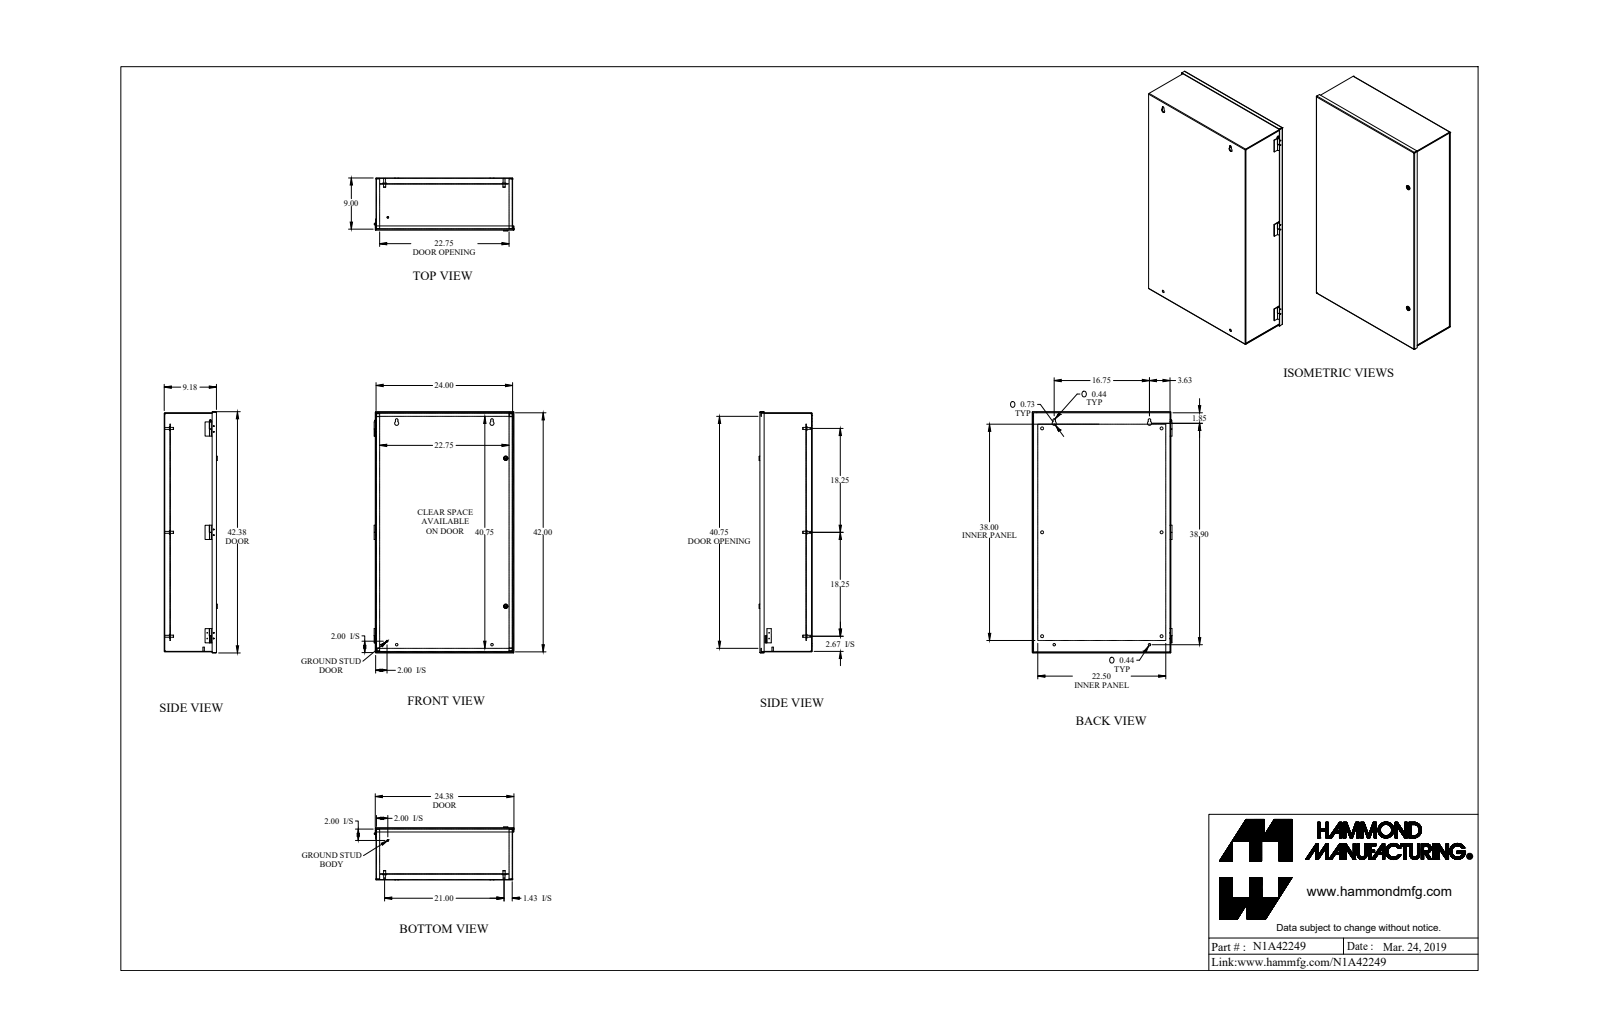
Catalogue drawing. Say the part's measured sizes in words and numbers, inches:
The part is named "N1A42249". Its 3-D file was written by "SolidWorks 2018 (AUTOMOTIVE_DESIGN)". It is 34 solids with 767 faces: 434 planar, 269 cylindrical and 64 other. Overall it measures 42.384 by 24.574 by 9.299 inches. Its volume is 312.8 cubic inches and its surface area 8 712 square inches. Round holes: 12 of diameter 0.14, 6 of diameter 0.5, 4 of diameter 0.307, 4 of diameter 0.445, 2 of diameter 0.437, 2 of diameter 0.516, 2 of diameter 0.734, 1 of diameter 0.17, 1 of diameter 0.187. Round bosses or shafts: 12 of diameter 0.128, 7 of diameter 0.375, 6 of diameter 0.65, 6 of diameter 0.33, 4 of diameter 1, 2 of diameter 0.788, 2 of diameter 0.535, 2 of diameter 0.496. Partial cylindrical surfaces (rounded edges, fillets, slot ends): 16 of radius 0.036, 16 of radius 0.108, 2 of radius 0.06, 2 of radius 0.125, 2 of radius 0.153, 2 of radius 0.219, 2 of radius 0.315, 1 of radius 0.03. The main face-to-face distances are 0.072, 9.105, 1.009, 8.096, 9.033, 9.177, 0.937, 1.081, 8.024, 8.168. The hole center spacings are 1, 1.119, 18.156, 18.25, 27.822, 21, 5.258, 13.003.
